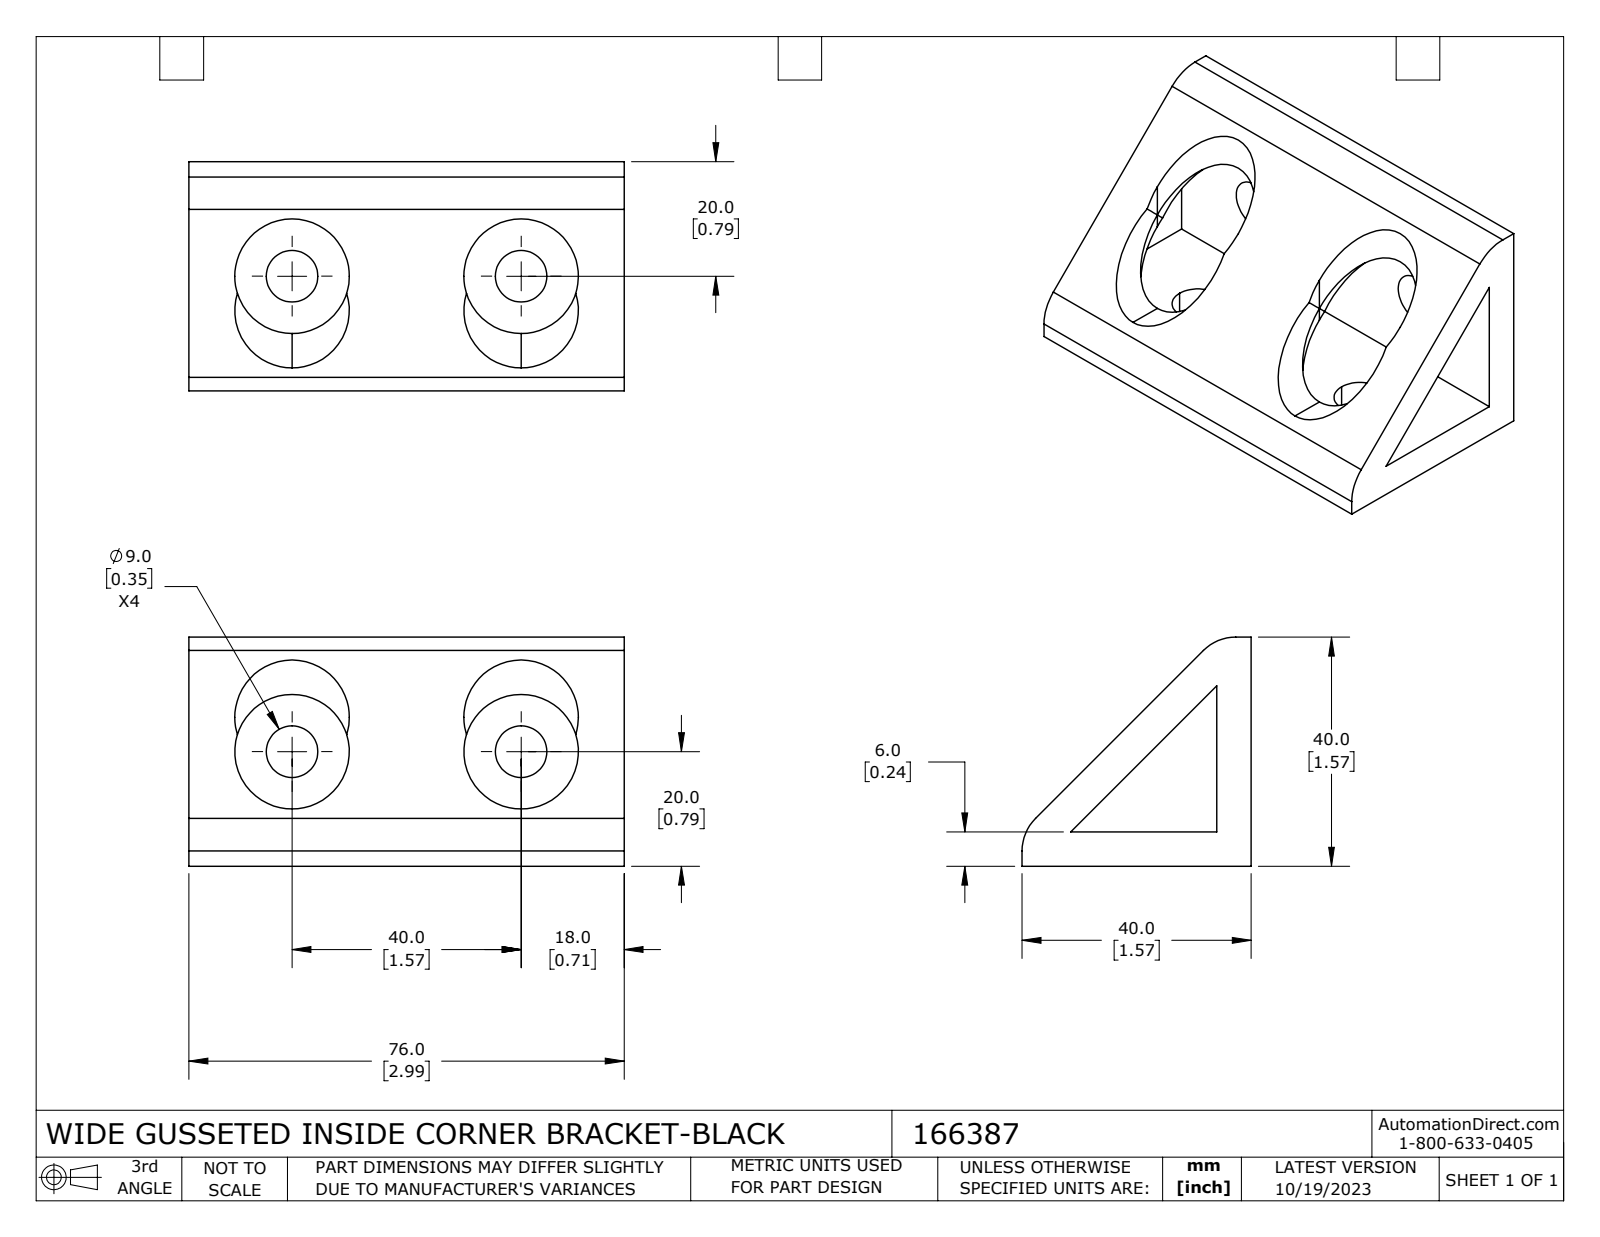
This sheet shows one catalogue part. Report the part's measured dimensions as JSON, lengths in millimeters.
{"part_name": "166387", "step_written_by": "SolidWorks 2023 (CONFIG_CONTROL_DESIGN)", "units": "millimeters", "bodies": {"solids": 1, "faces": 38, "planar": 10, "cylindrical": 28, "other": 0}, "overall_size": [76, 40, 40], "volume_mm3": 45031, "surface_area_mm2": 17669, "round_holes": [[9, 4], [20, 4]], "partial_cylinders_radius": [[8, 2]], "face_to_face_distances": [6, 76, 40, 34], "hole_center_spacings": [40]}
